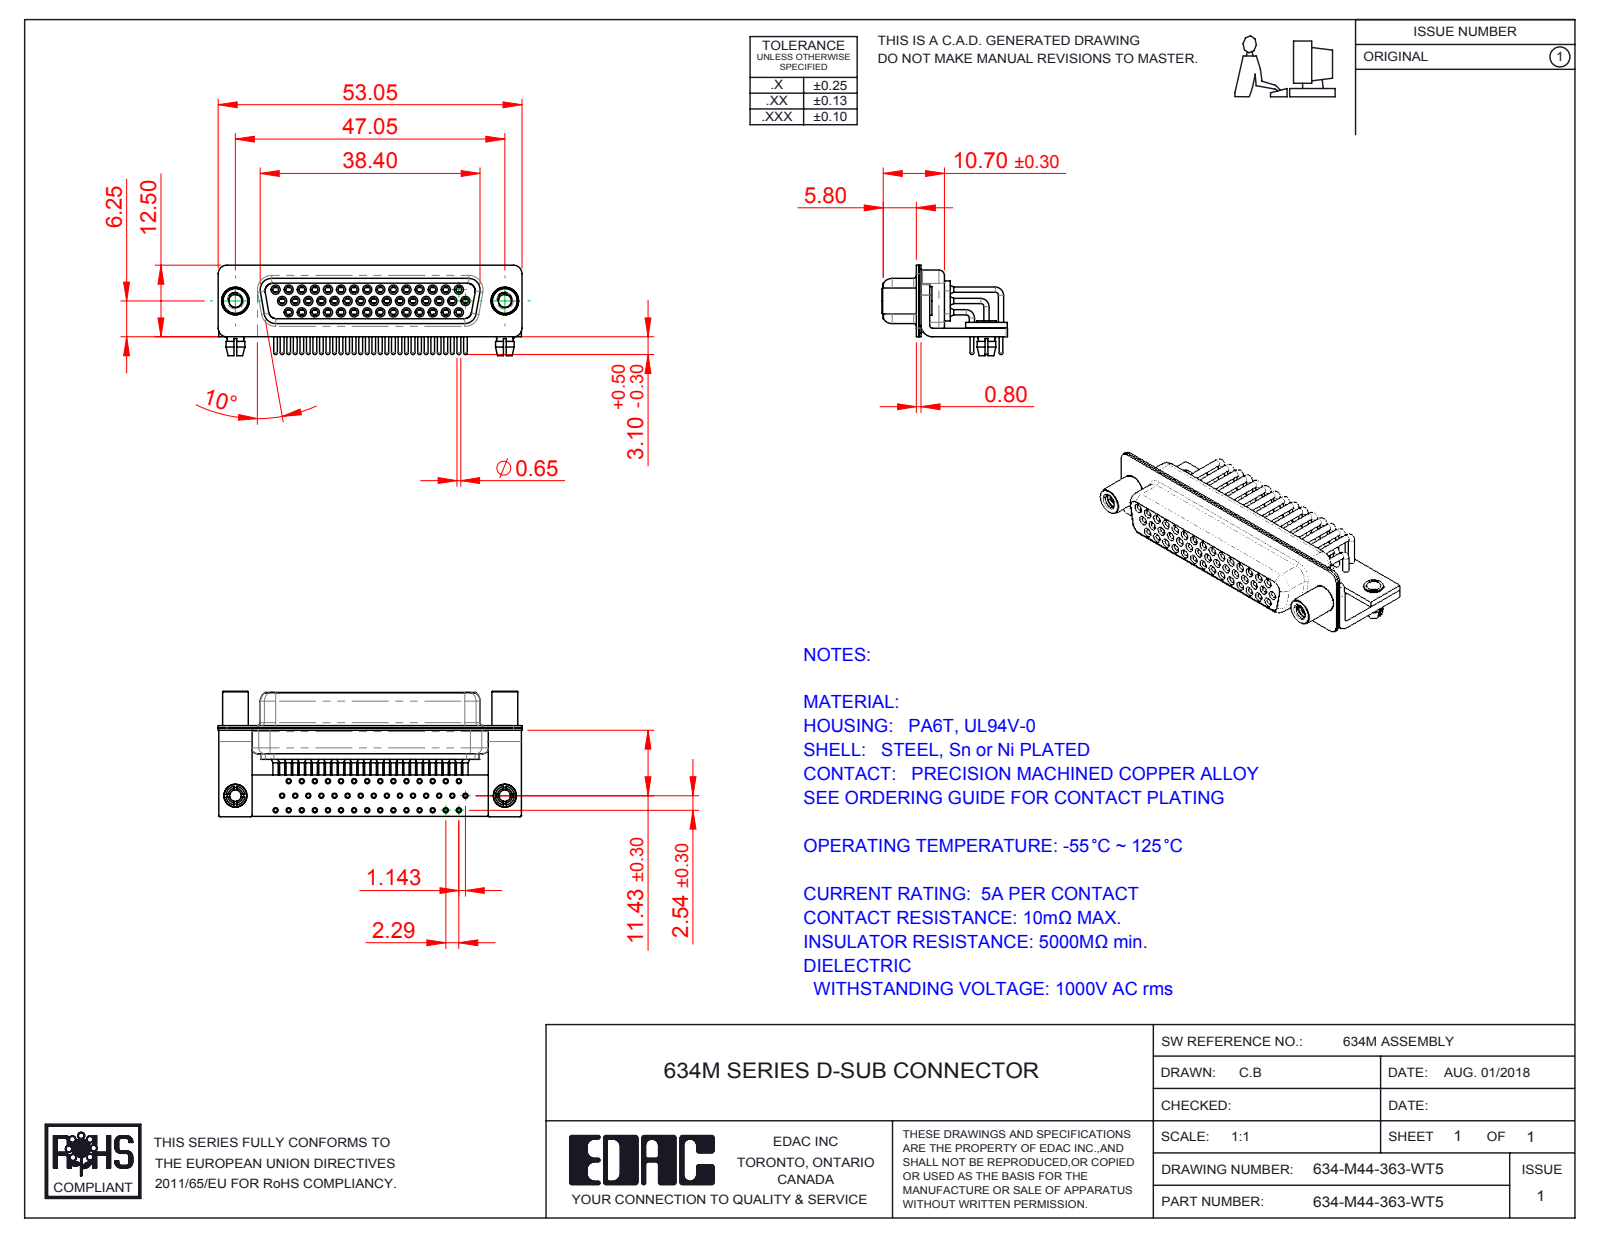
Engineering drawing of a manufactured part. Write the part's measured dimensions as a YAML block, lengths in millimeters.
part_name: "634M 4-40 Threaded Standoff; 634M Contact Row 2; 634M Board Lock; 634M Contact Row 3 (+7 more)"
step_written_by: "SolidWorks 2016 (CONFIG_CONTROL_DESIGN)"
units: millimeters
bodies: {solids: 54, faces: 2891, planar: 803, cylindrical: 1333, other: 755}
overall_size: [53.05, 21.9, 15.8]
volume: 4630
surface_area: 15156
round_holes:
  - {diameter: 2, count: 46}
  - {diameter: 0.9, count: 44}
  - {diameter: 1, count: 44}
  - {diameter: 1.1, count: 44}
  - {diameter: 1.7, count: 44}
  - {diameter: 1.8, count: 44}
  - {diameter: 2.26, count: 2}
  - {diameter: 2.5, count: 2}
  - {diameter: 3.2, count: 2}
  - {diameter: 4, count: 2}
  - {diameter: 4.8, count: 2}
round_bosses_or_shafts:
  - {diameter: 1.6, count: 44}
  - {diameter: 1.5, count: 44}
  - {diameter: 0.9, count: 44}
  - {diameter: 0.65, count: 44}
  - {diameter: 5, count: 2}
  - {diameter: 4.9, count: 2}
  - {diameter: 4.5, count: 2}
  - {diameter: 4, count: 2}
partial_cylinders:
  - {radius: 0.25, count: 16}
  - {radius: 1.5, count: 16}
  - {radius: 2, count: 13}
  - {radius: 1.35, count: 8}
  - {radius: 1.6, count: 8}
  - {radius: 0.5, count: 5}
  - {radius: 0.6, count: 4}
  - {radius: 0.65, count: 4}
face_to_face_distances: [0.4, 2.3, 1.9, 1, 0.8, 9.35, 8.5, 1.5, 1.45, 8.95]
hole_center_spacings: [2.28, 2.29, 4.57, 6.86, 11.43, 3.96, 8.24, 9.14]
